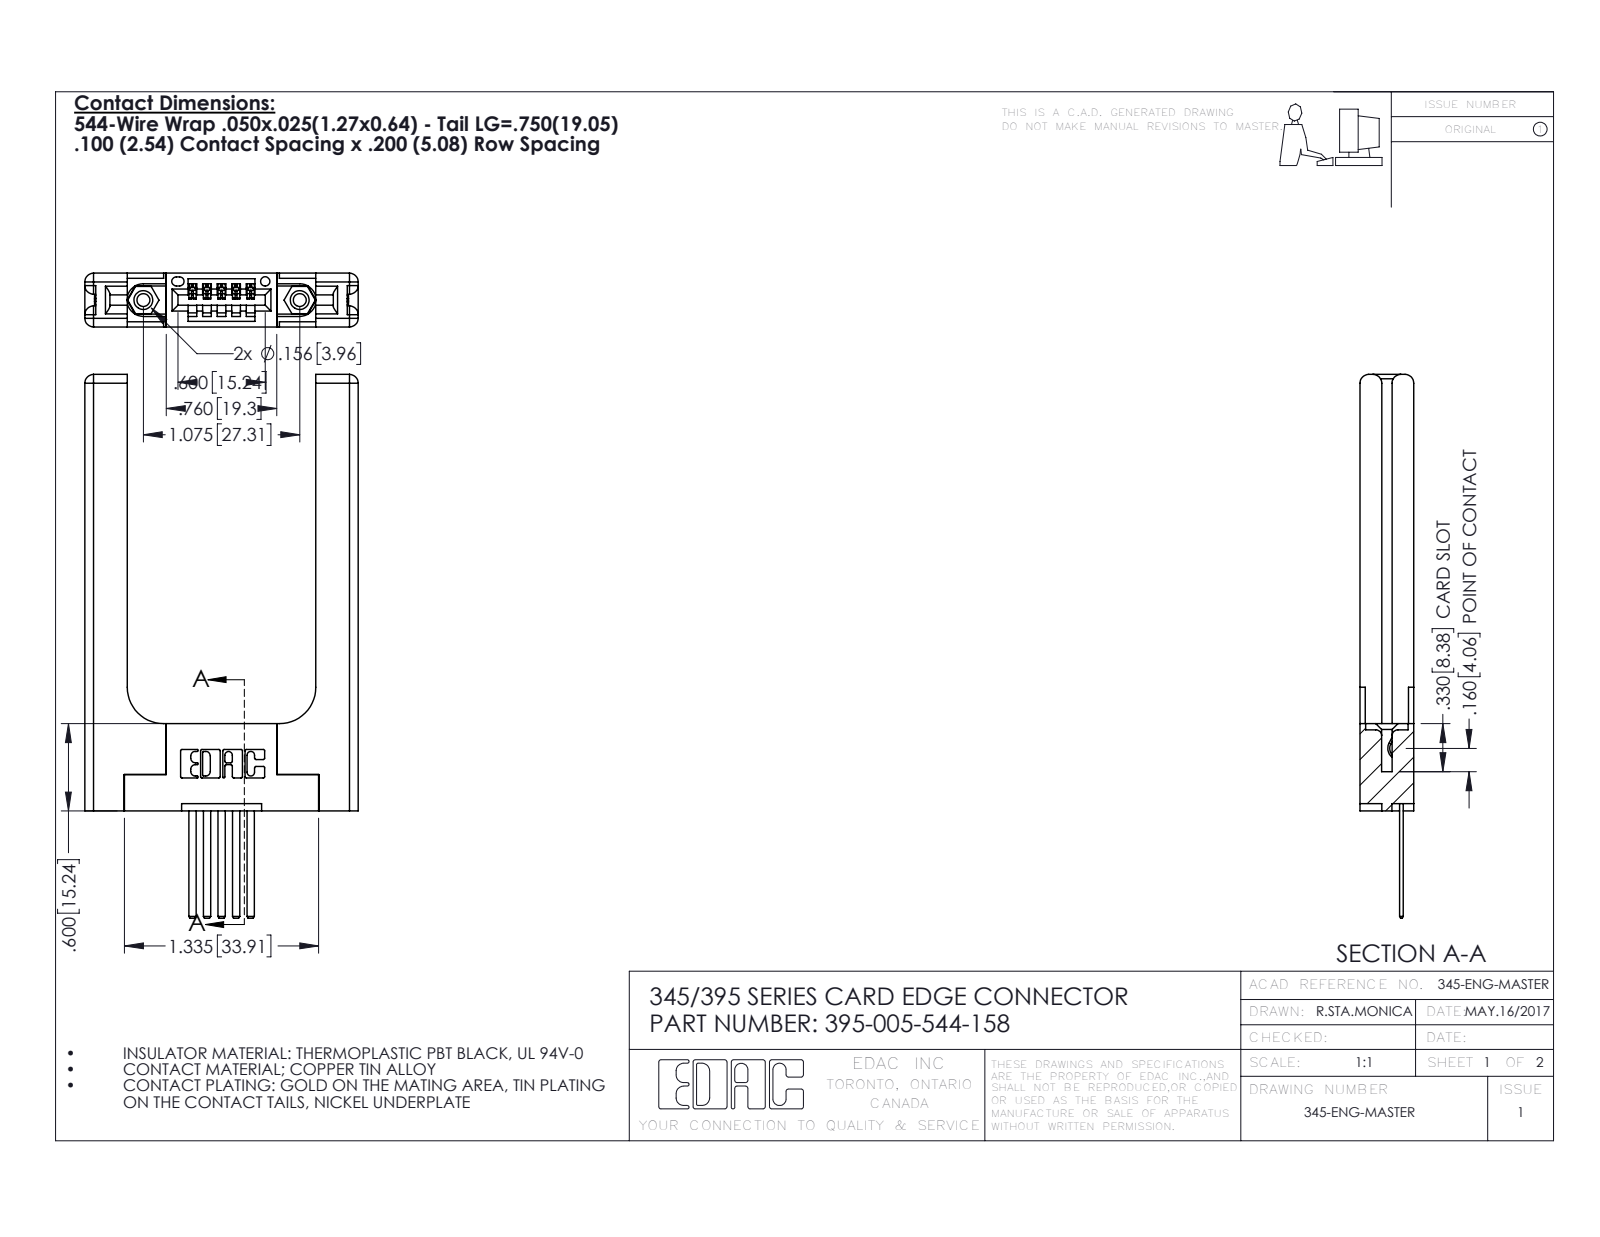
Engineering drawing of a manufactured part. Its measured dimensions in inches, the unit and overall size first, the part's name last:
Units: inches
Overall size (bounding box): 3.737 × 1.879 × 0.37
Round holes (diameter × count): ⌀0.089 ×2, ⌀0.125 ×2, ⌀0.156 ×2, ⌀0.064 ×1
Round bosses / shafts (diameter × count): ⌀0.155 ×2
Partial cylindrical surfaces — rounded edges, fillets, slot ends (radius × count): R0.01 ×22, R0.06 ×16, R0.006 ×10, R0.007 ×6, R0.031 ×6, R0.026 ×3, R0.03 ×2, R0.031 ×2
Main face-to-face distances: 0.37, 0.15, 0.22, 0.072, 0.077, 0.148, 0.298, 1.296, 0.071, 0.2
Hole centre spacings: 0.27, 0.847, 1.075
Volume: 0.781 in³ · Surface area: 16.55 in²
Bodies: 10 solids, 642 faces (408 planar, 174 cylindrical, 60 other)
Part name (STEP PRODUCT): 395-005-544-158; 345-220-058_345-220-058; 345-292-001_345-293-144; 345-250-001_345-250-001-102 (+1 more)
STEP written by: SolidWorks 2016 (CONFIG_CONTROL_DESIGN)
